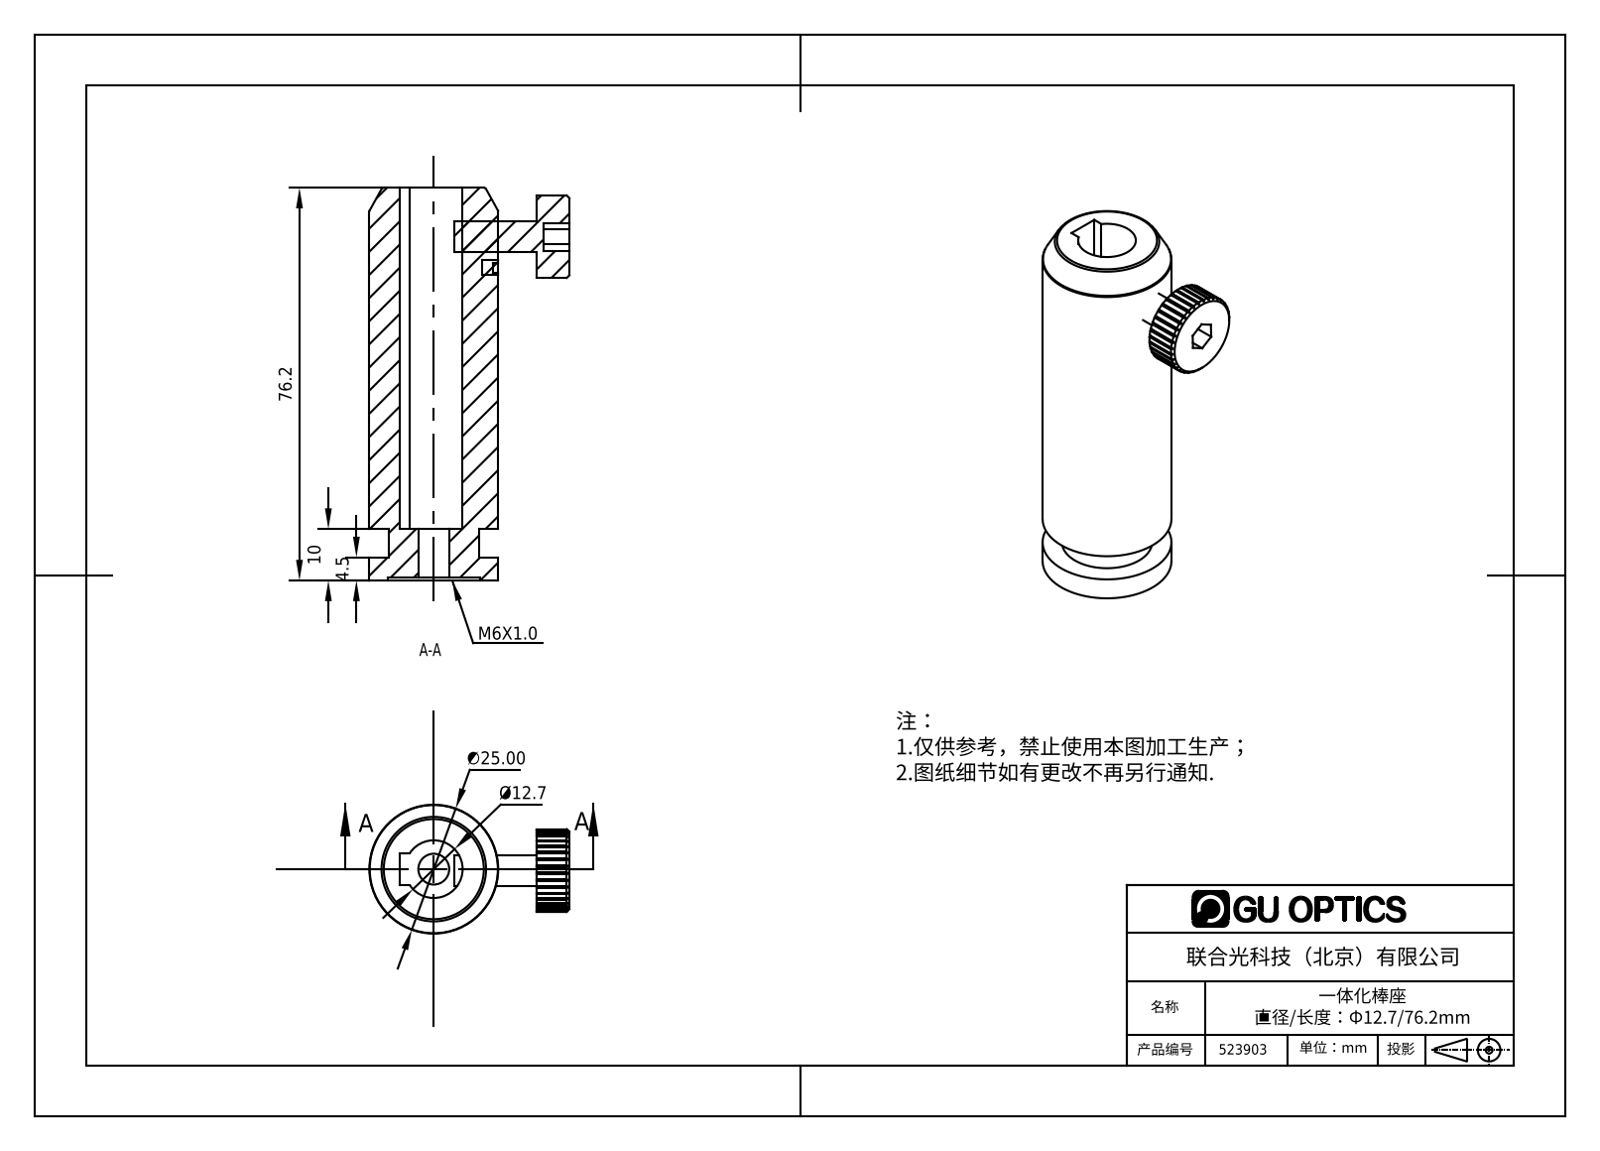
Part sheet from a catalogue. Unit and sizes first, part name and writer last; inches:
Units: inches
Overall size (bounding box): 3 × 1.528 × 0.984
Round holes (diameter × count): ⌀0.235 ×1, ⌀0.441 ×1, ⌀0.709 ×1
Round bosses / shafts (diameter × count): ⌀0.984 ×1, ⌀0.689 ×1, ⌀0.236 ×1, ⌀0.118 ×1
Partial cylindrical surfaces — rounded edges, fillets, slot ends (radius × count): R0.315 ×1
Main face-to-face distances: 0.217, 0.177, 0.394, 0.02, 0.157, 0.374, 3, 2.98, 2.823, 2.606
Bodies: 0 solids, 161 faces (99 planar, 54 cylindrical, 8 other)
Part name (STEP PRODUCT): 523903
STEP written by: SolidWorks 2016 (AUTOMOTIVE_DESIGN)
